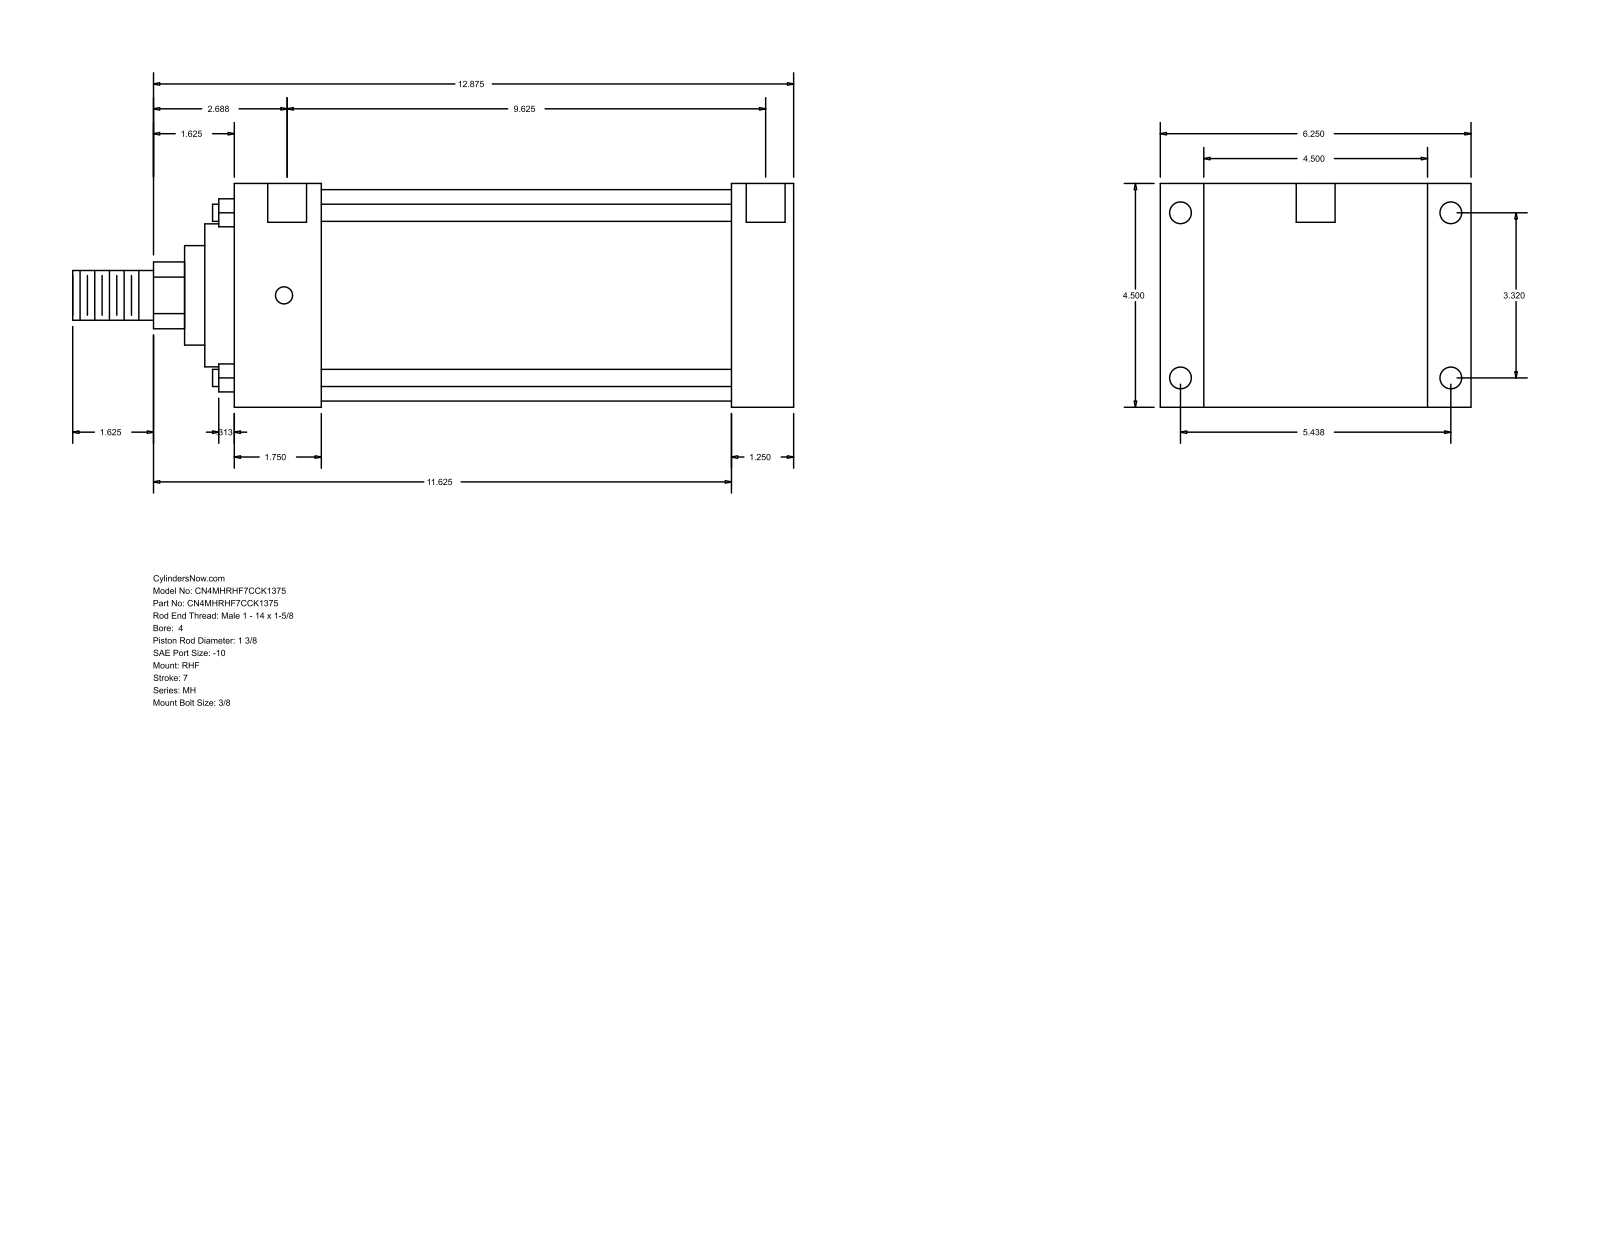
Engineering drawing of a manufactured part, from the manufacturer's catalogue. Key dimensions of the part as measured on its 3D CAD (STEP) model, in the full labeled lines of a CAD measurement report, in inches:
Part name (STEP PRODUCT): MH_RHF__0400_1.375
STEP written by: GSSL Pune (CONFIG_CONTROL_DESIGN)
Units: inches
Bodies: 0 solids, 90 faces (61 planar, 29 cylindrical, 0 other)
Overall size (bounding box): 14.5 × 6.25 × 4.5
Round holes (diameter × count): ⌀0.344 ×4, ⌀0.438 ×4, ⌀0.781 ×2
Round bosses / shafts (diameter × count): ⌀0.345 ×4, ⌀4.25 ×1, ⌀2.875 ×1, ⌀2 ×1, ⌀1.375 ×1, ⌀1 ×1
Partial cylindrical surfaces — rounded edges, fillets, slot ends (radius × count): R0.672 ×1
Main face-to-face distances: 4.5, 1.25, 10, 11.25, 0.875, 5.375, 1.75, 8.25, 9.5, 6.25
Hole centre spacings: 3.32, 5.438, 6.371, 9.75, 0.062, 0.063, 9.625, 9.687
